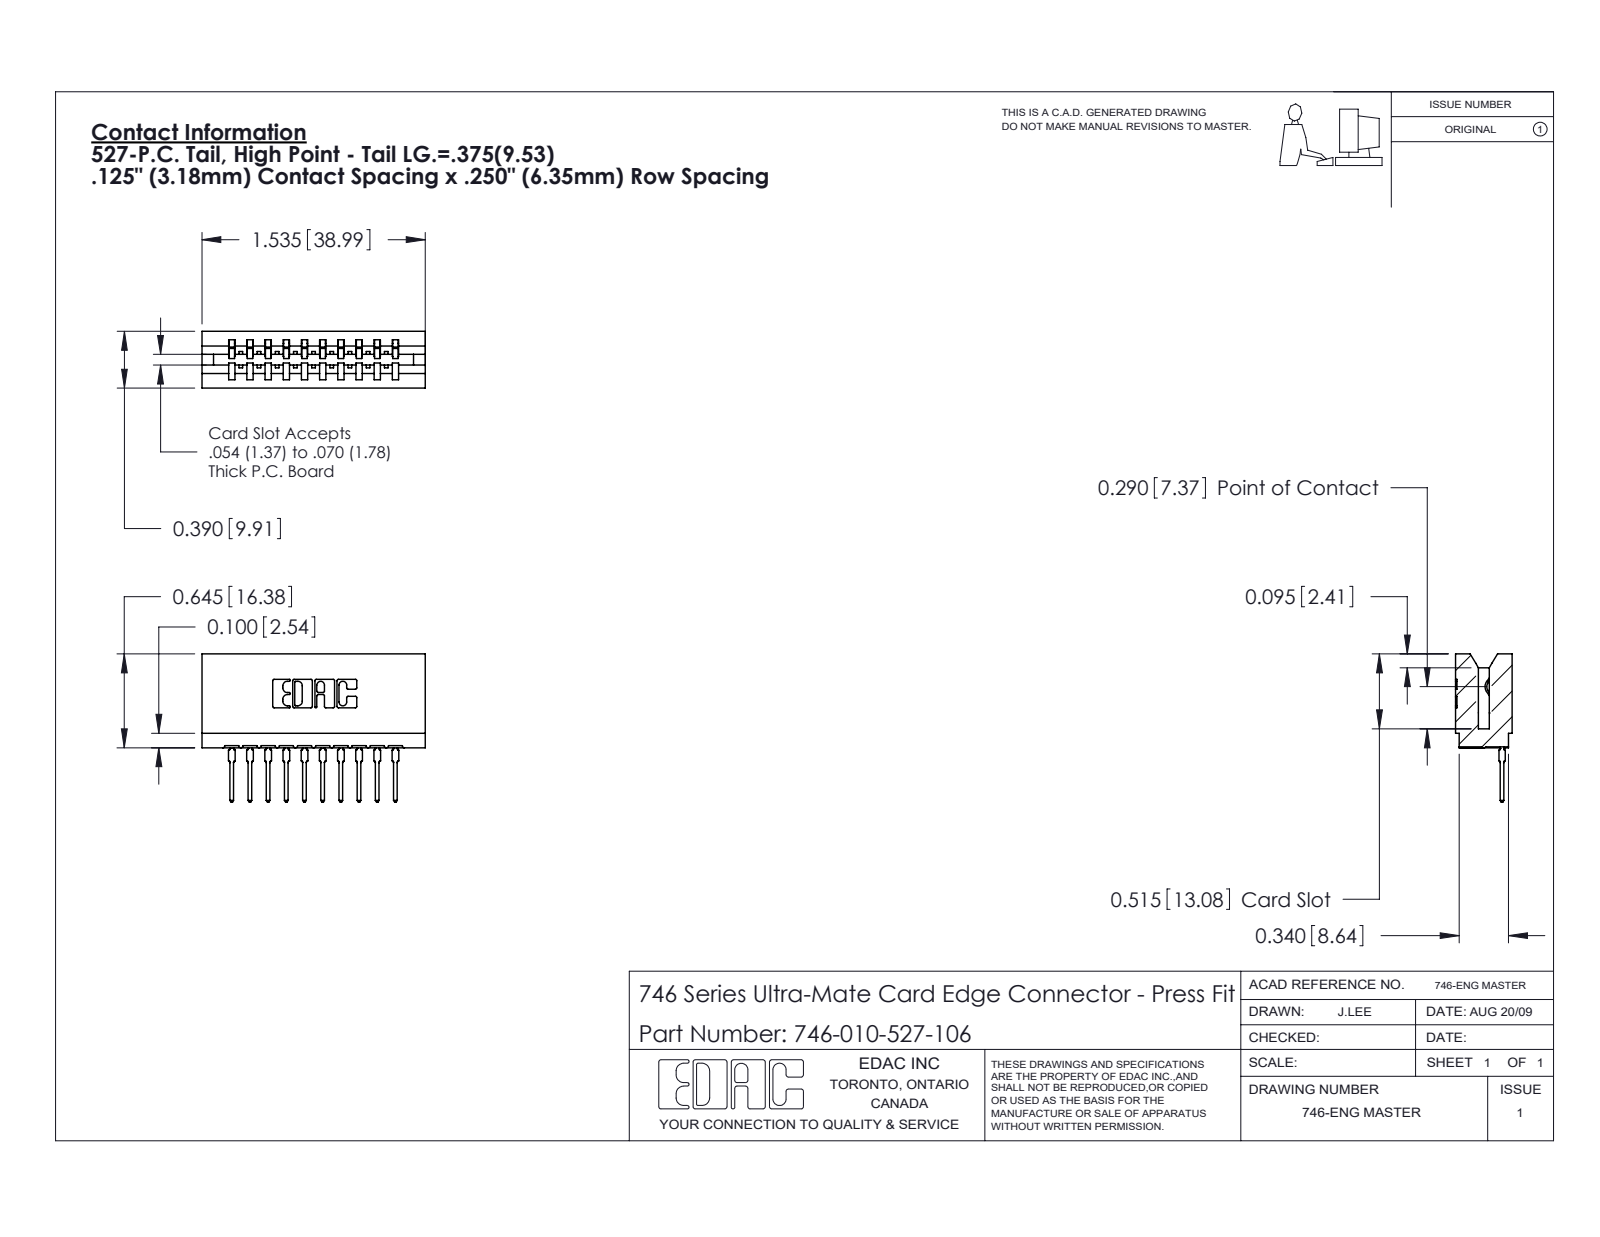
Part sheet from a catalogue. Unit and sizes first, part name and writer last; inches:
Units: inches
Overall size (bounding box): 1.535 × 1.019 × 0.39
Partial cylindrical surfaces — rounded edges, fillets, slot ends (radius × count): R0.01 ×22, R0.021 ×20, R0.015 ×11, R0.007 ×6, R0.031 ×6, R0.005 ×4, R0.011 ×4, R0.026 ×3
Main face-to-face distances: 0.25, 0.333, 0.5, 0.042, 0.125, 0.057, 0.292, 0.75, 0.39, 0.375
Volume: 0.261 in³ · Surface area: 9.108 in²
Bodies: 11 solids, 1178 faces (686 planar, 232 cylindrical, 260 other)
Part name (STEP PRODUCT): 746-010-527-106; 746-292-001_527; 746 Part_.515 Slot Depth - 06
STEP written by: SolidWorks 2020 (CONFIG_CONTROL_DESIGN)
